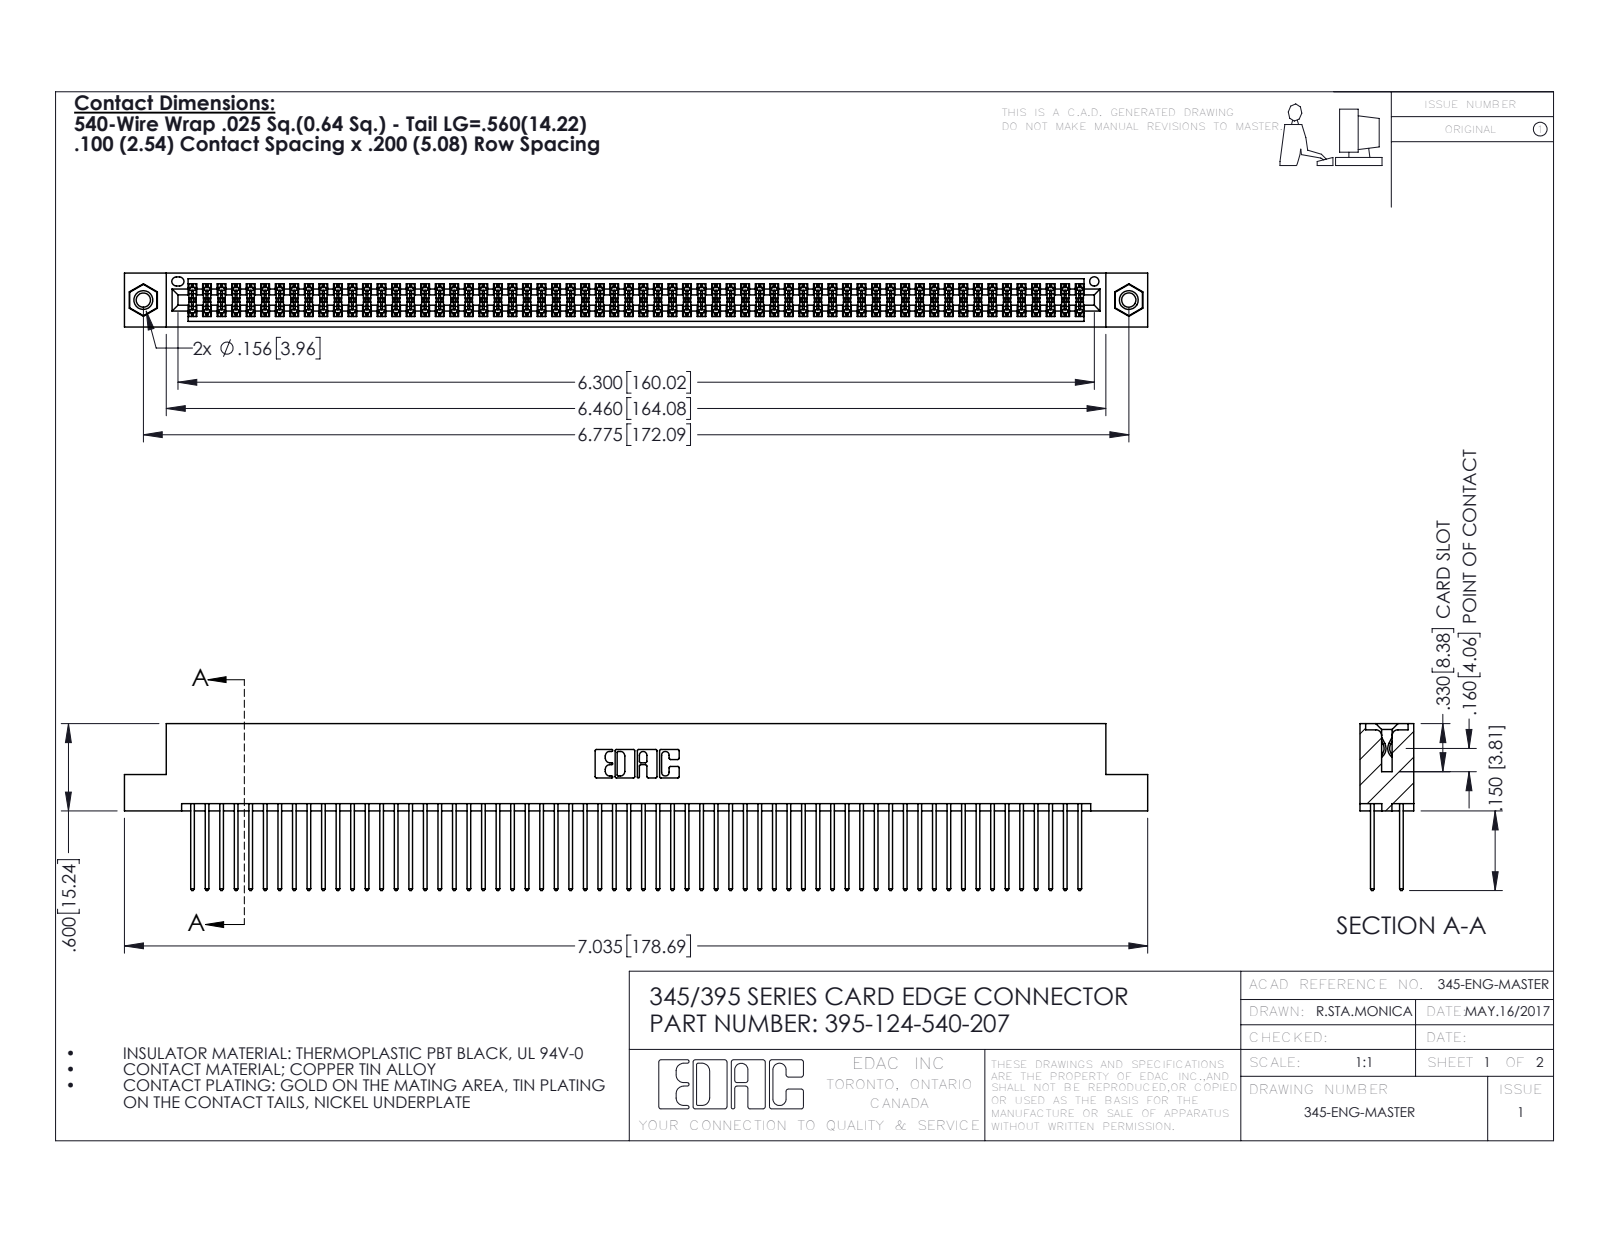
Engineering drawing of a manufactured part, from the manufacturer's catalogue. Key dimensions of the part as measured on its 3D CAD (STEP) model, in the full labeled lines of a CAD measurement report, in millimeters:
Part name (STEP PRODUCT): 345-292-001_345-293-140; 345-250-001_345-250-005-103; 345 Part_Flush Mounting Lugs - 0.156 Dia-TI; 395-124-540-207
STEP written by: SolidWorks 2016 (CONFIG_CONTROL_DESIGN)
Units: millimetres
Bodies: 127 solids, 6386 faces (4204 planar, 2166 cylindrical, 16 other)
Overall size (bounding box): 178.7 × 29.1 × 9.4
Volume: 17 990 mm³ · Surface area: 29 210 mm²
Round holes (diameter × count): ⌀2.5 ×2, ⌀3.2 ×2, ⌀4 ×2, ⌀1.6 ×1
Round bosses / shafts (diameter × count): ⌀3.9 ×2
Partial cylindrical surfaces — rounded edges, fillets, slot ends (radius × count): R0.2 ×186, R0.3 ×124, R0.3 ×22, R0.2 ×6, R0.8 ×6, R0.7 ×3, R0.4 ×2, R0.5 ×2
Main face-to-face distances: 1.8, 7.6, 5.1, 2.5, 6.9, 0.6, 9.4, 5.7, 4.4, 3.8
Hole centre spacings: 6.9, 166.1, 172.1
